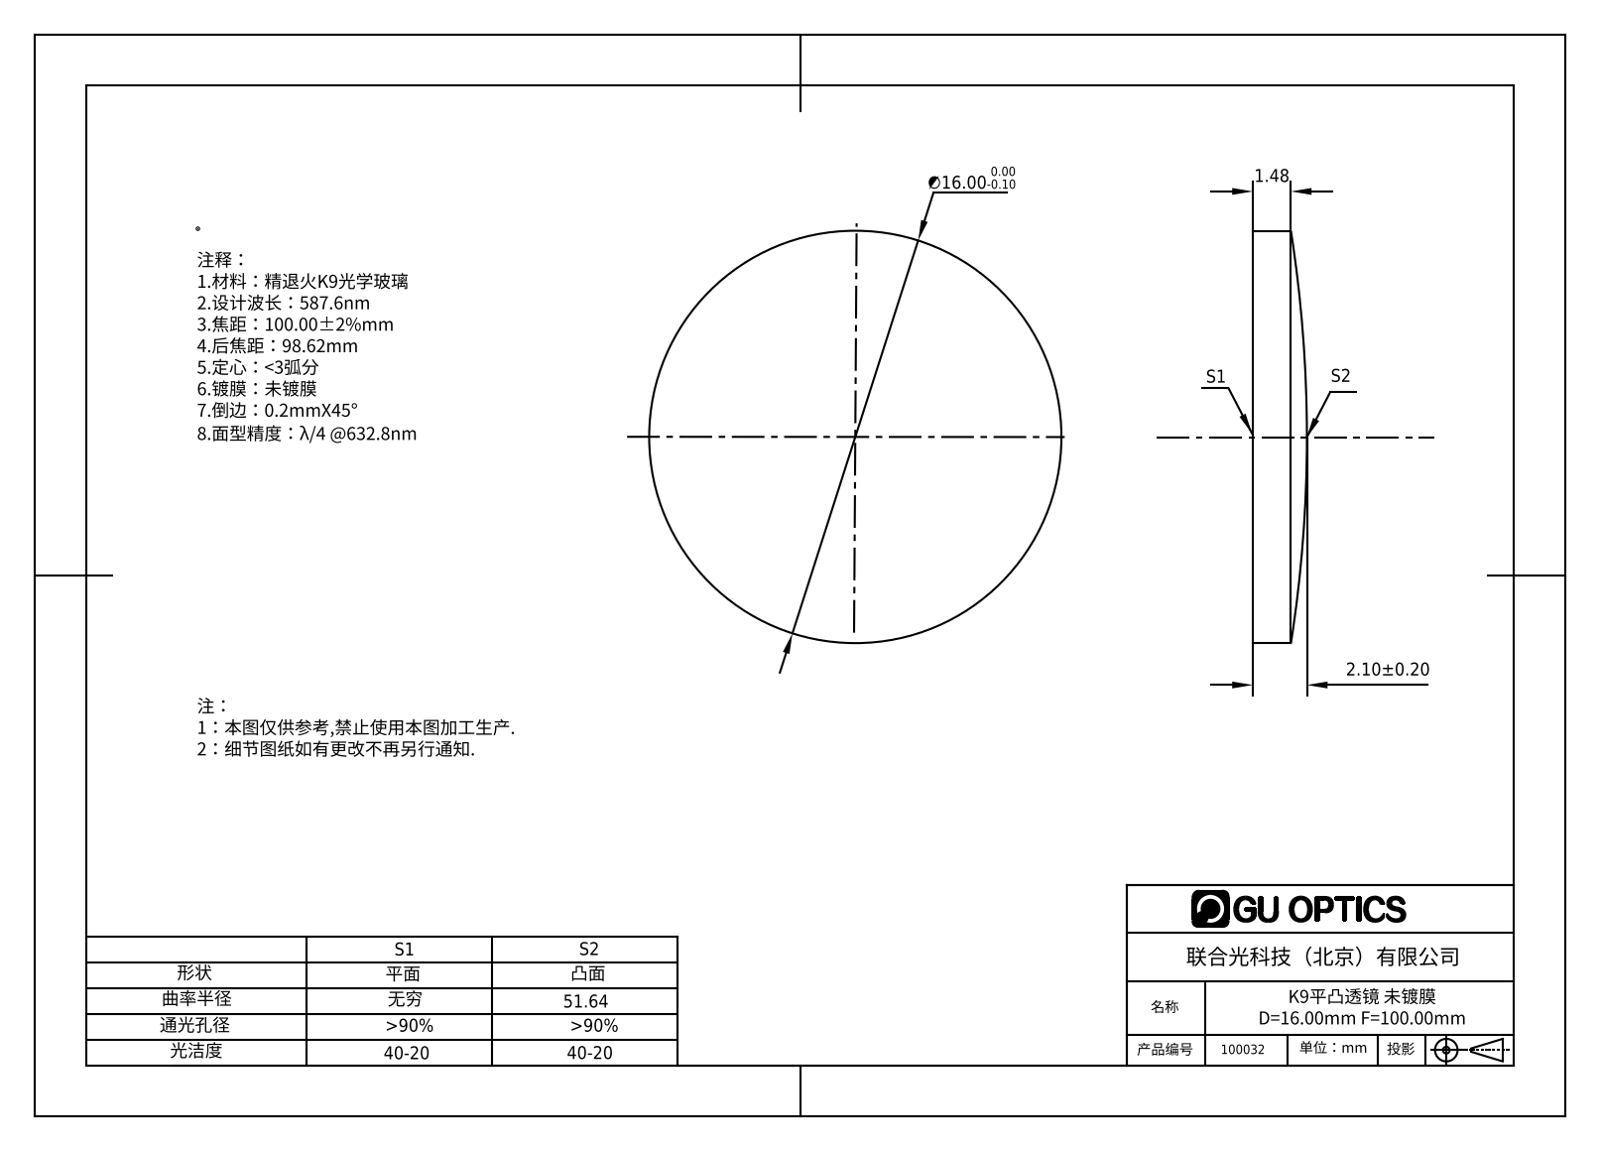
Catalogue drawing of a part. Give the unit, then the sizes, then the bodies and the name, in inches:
Units: inches
Overall size (bounding box): 0.63 × 0.63 × 0.083
Round bosses / shafts (diameter × count): ⌀0.63 ×1
Volume: 0.022 in³ · Surface area: 0.741 in²
Bodies: 1 solid, 5 faces (1 planar, 2 cylindrical, 2 other)
Part name (STEP PRODUCT): 100032
STEP written by: SolidWorks 2016 (AUTOMOTIVE_DESIGN)
